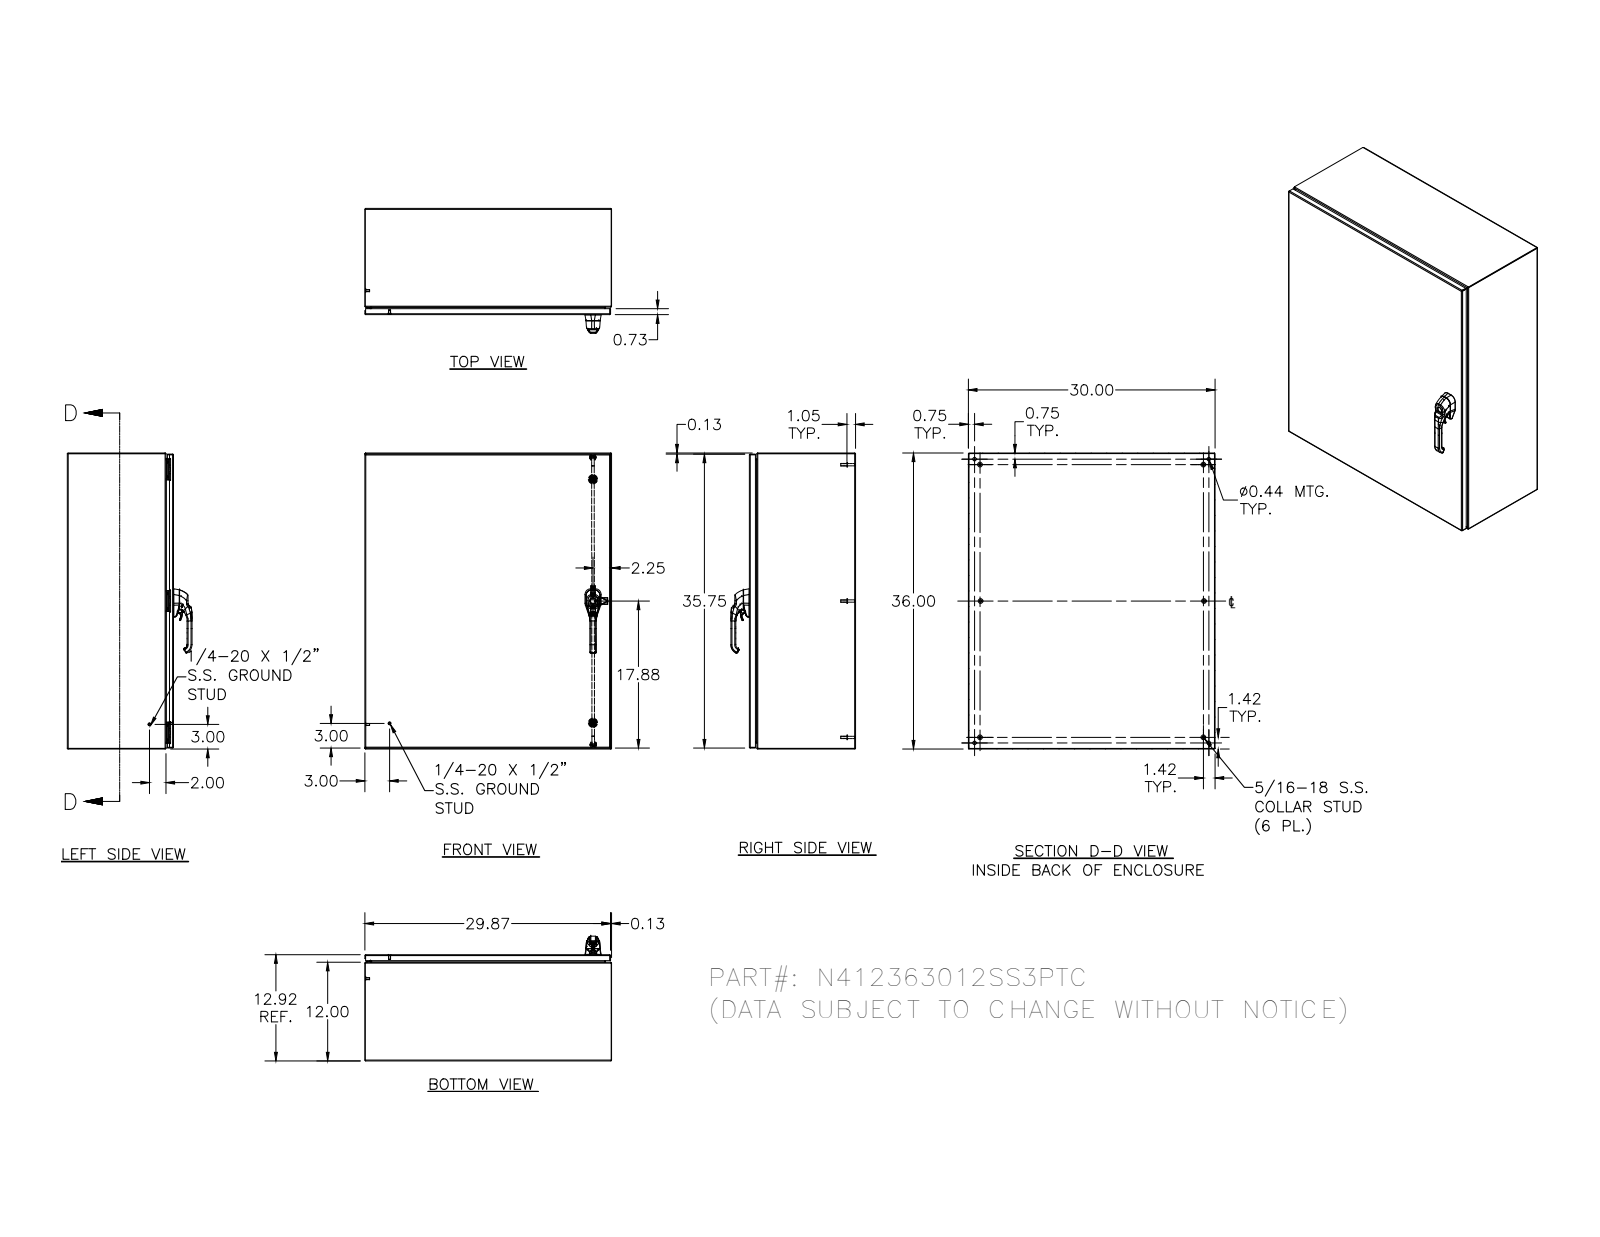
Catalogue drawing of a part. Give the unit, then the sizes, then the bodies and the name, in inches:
Units: inches
Overall size (bounding box): 36 × 30 × 15.166
Round holes (diameter × count): ⌀0.093 ×6, ⌀0.152 ×6, ⌀0.165 ×6, ⌀0.167 ×6, ⌀0.172 ×6, ⌀0.188 ×6, ⌀0.197 ×4, ⌀0.437 ×4, ⌀0.156 ×3, ⌀0.213 ×3, ⌀0.106 ×2, ⌀0.16 ×2
Round bosses / shafts (diameter × count): ⌀0.25 ×14, ⌀0.591 ×6, ⌀0.563 ×6, ⌀0.36 ×6, ⌀0.32 ×6, ⌀0.3 ×6, ⌀0.275 ×6, ⌀0.256 ×6
Partial cylindrical surfaces — rounded edges, fillets, slot ends (radius × count): R0.02 ×186, R0.012 ×100, R0.05 ×38, R0.031 ×34, R0.016 ×26, R0.019 ×23, R0.118 ×23, R0.125 ×21
Main face-to-face distances: 0.074, 12.843, 12.769, 12.917, 29.926, 35.926, 29.852, 30, 36, 35.852
Hole centre spacings: 16, 15.996, 31.996, 16.008, 0.017, 0.66, 16.656, 32
Volume: 308.1 in³ · Surface area: 8 204 in²
Bodies: 74 solids, 3522 faces (1171 planar, 1295 cylindrical, 1056 other)
Part name (STEP PRODUCT): N412363012SS3PTC; N412363012SS3PTCBKP; N4123630SS3PTCLID; HFW328176 (+8 more)
STEP written by: Autodesk Inventor 2011 (AUTOMOTIVE_DESIGN)
